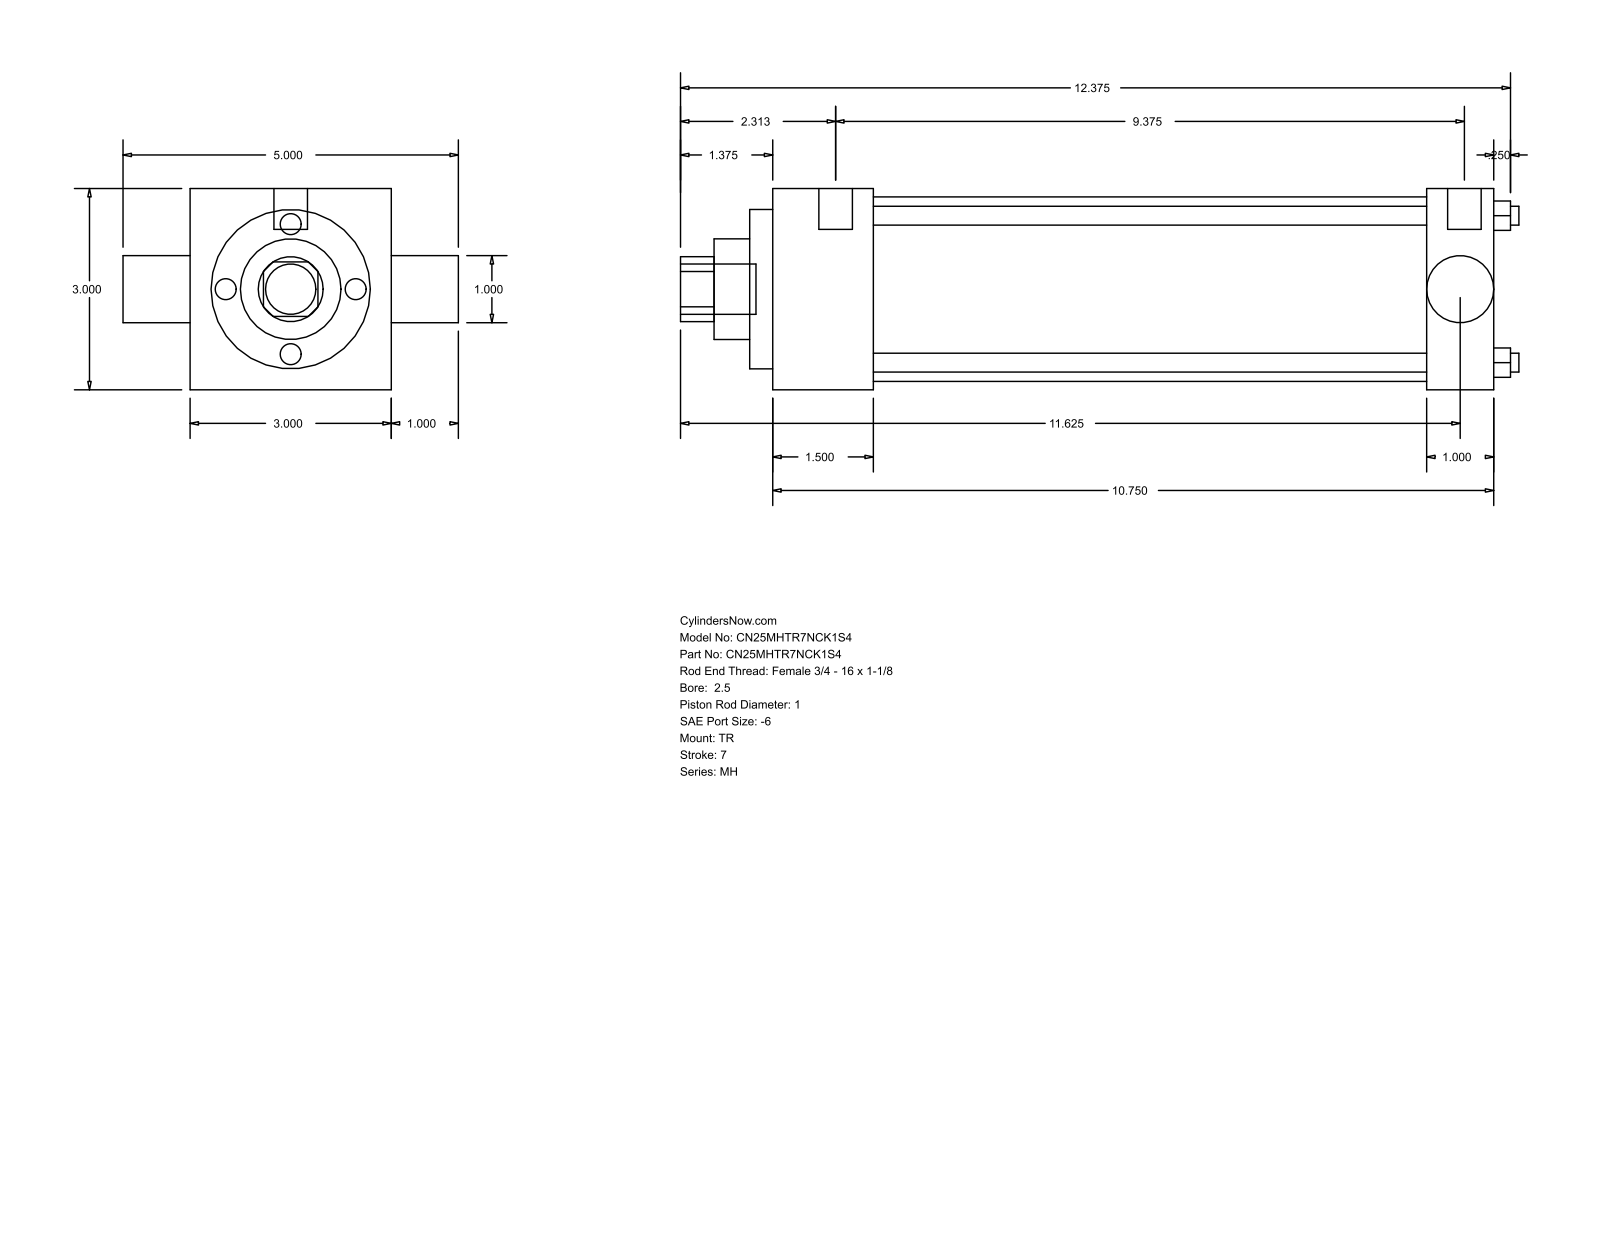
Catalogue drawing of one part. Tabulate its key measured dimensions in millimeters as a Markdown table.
| quantity | value |
| --- | --- |
| part name | MH_TR__0250_1 |
| STEP written by | GSSL Pune (CONFIG_CONTROL_DESIGN) |
| units | millimeters |
| bodies | 0 solids, 86 faces (61 planar, 25 cylindrical, 0 other) |
| overall size | 317.5 × 127 × 76.2 |
| round holes (diameter × count) | 7.14 × 4, 25.35 × 1, 25.4 × 1, 38.1 × 1, 60.33 × 1, 69.85 × 1 |
| round bosses / shafts (diameter × count) | 5.56 × 3, 12.7 × 2, 19.05 × 1 |
| partial cylindrical surfaces (radius × count) | 12.29 × 1 |
| main face-to-face distances | 76.2, 273.06, 38.11, 234.95, 247.65, 209.54, 25.41, 8.73, 46.84, 256.38 |
| hole center spacings | 39.33, 55.62, 78.66 |
